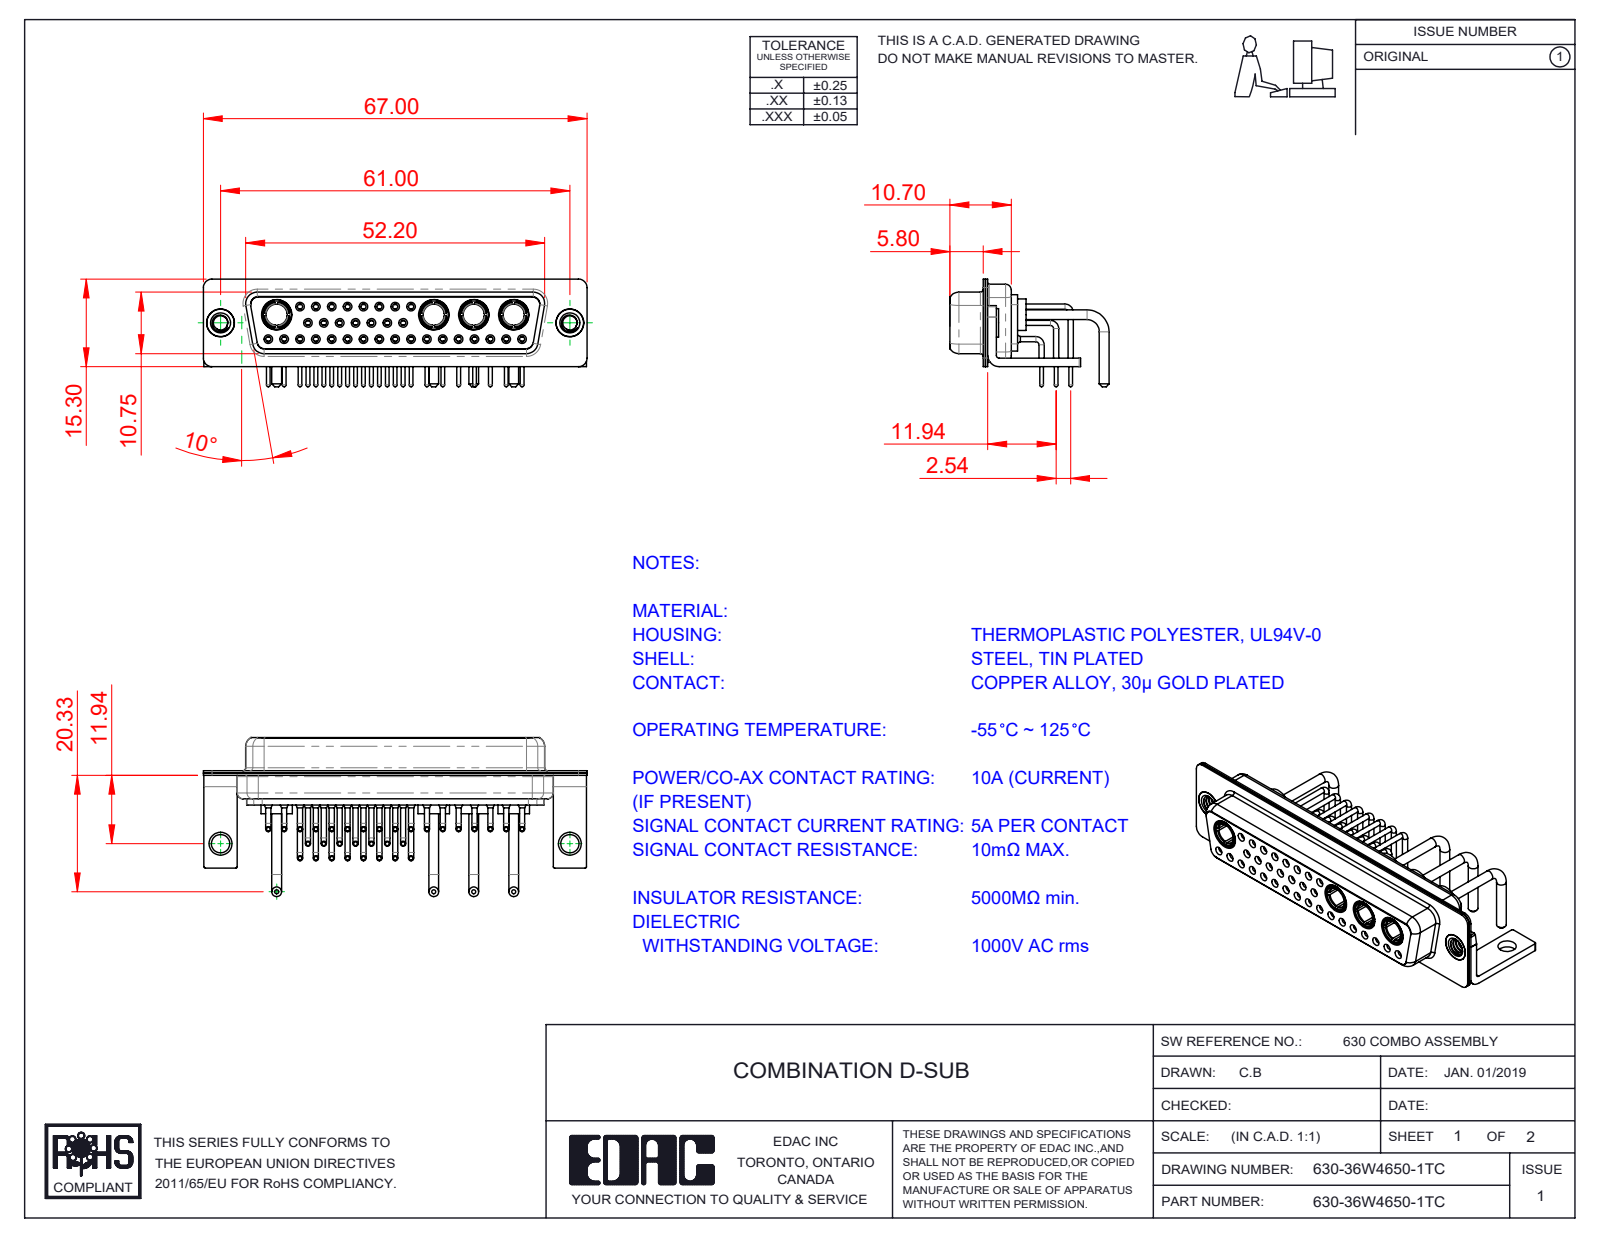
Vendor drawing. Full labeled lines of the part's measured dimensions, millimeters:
Part name (STEP PRODUCT): Power Socket_Ext 10A RA 50; 630Combo Shell Rear_50 Contacts; 630Combo Contact Row 3; 630-36W4650-1TC (+6 more)
STEP written by: SolidWorks 2020 (CONFIG_CONTROL_DESIGN)
Units: millimetres
Bodies: 47 solids, 2325 faces (683 planar, 991 cylindrical, 651 other)
Overall size (bounding box): 67 × 27.78 × 18.8
Volume: 7 357 mm³ · Surface area: 16 235 mm²
Round holes (diameter × count): ⌀0.9 ×32, ⌀1.1 ×32, ⌀1.5 ×32, ⌀2 ×32, ⌀1.6 ×24, ⌀1.7 ×8, ⌀4.85 ×6, ⌀3.7 ×4, ⌀5.3 ×4, ⌀2.5 ×2, ⌀3.2 ×2, ⌀4 ×2
Round bosses / shafts (diameter × count): ⌀0.9 ×33, ⌀0.65 ×32, ⌀1.6 ×9, ⌀1.7 ×8, ⌀5.5 ×4, ⌀5.2 ×4, ⌀4.96 ×4, ⌀4.75 ×4
Partial cylindrical surfaces — rounded edges, fillets, slot ends (radius × count): R0.25 ×16, R1.5 ×16, R2 ×13, R1.35 ×12, R1.6 ×8, R0.5 ×5, R0.6 ×4, R0.65 ×4
Main face-to-face distances: 0.4, 1.5, 5.2, 0.8, 6, 5.6, 5.8, 11.28, 1.82, 10.35
Hole centre spacings: 2.77, 5.54, 3.16, 8.31, 11.08, 13.85, 16.62, 19.39
